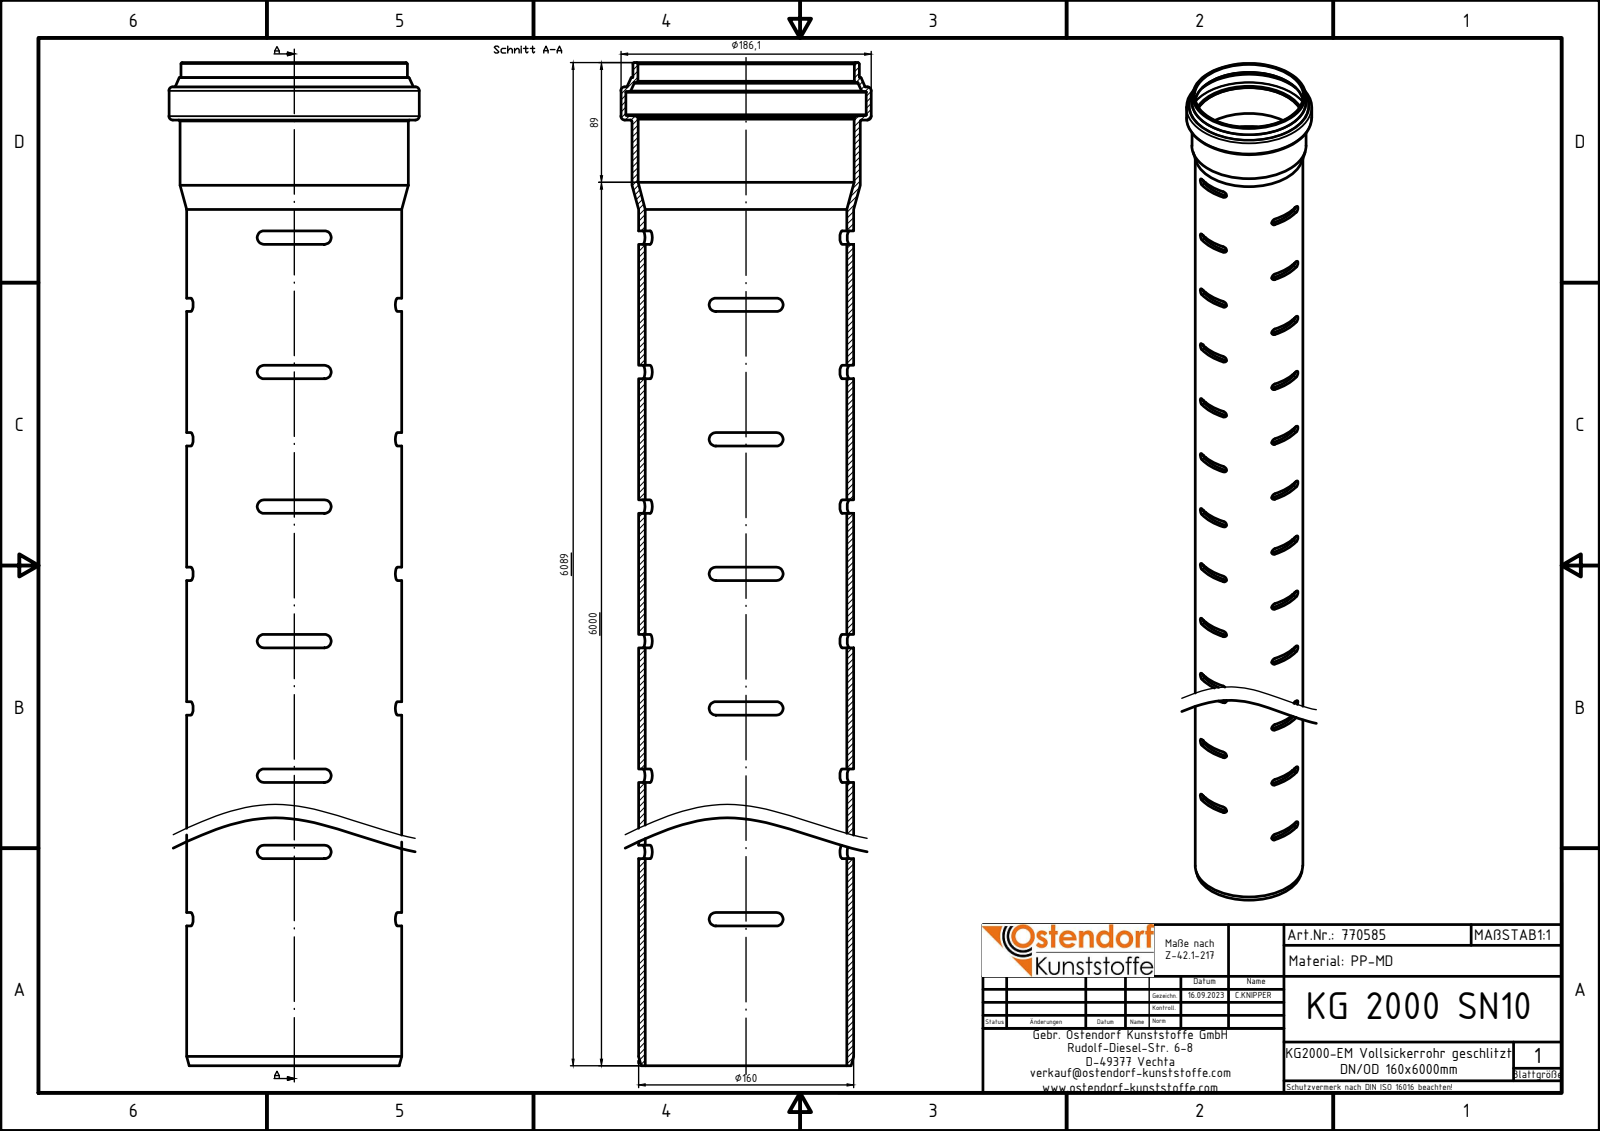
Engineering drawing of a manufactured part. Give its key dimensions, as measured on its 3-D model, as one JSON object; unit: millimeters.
{"part_name": "770585z", "step_written_by": "Autodesk Inventor 2024 (AUTOMOTIVE_DESIGN)", "units": "millimeters", "bodies": {"solids": 1, "faces": 981, "planar": 478, "cylindrical": 481, "other": 22}, "overall_size": [6089, 186.1, 186.1], "volume_mm3": 14390000, "surface_area_mm2": 5848000, "round_holes": [[149.85, 1], [160.6, 1], [161, 1], [178.7, 1]], "round_bosses_or_shafts": [[186.1, 1], [169.6, 1], [168.4, 1], [160, 1]], "partial_cylinders_radius": [[5, 236]], "face_to_face_distances": [100, 200, 300, 400, 500, 600, 700, 800, 900, 1000]}
